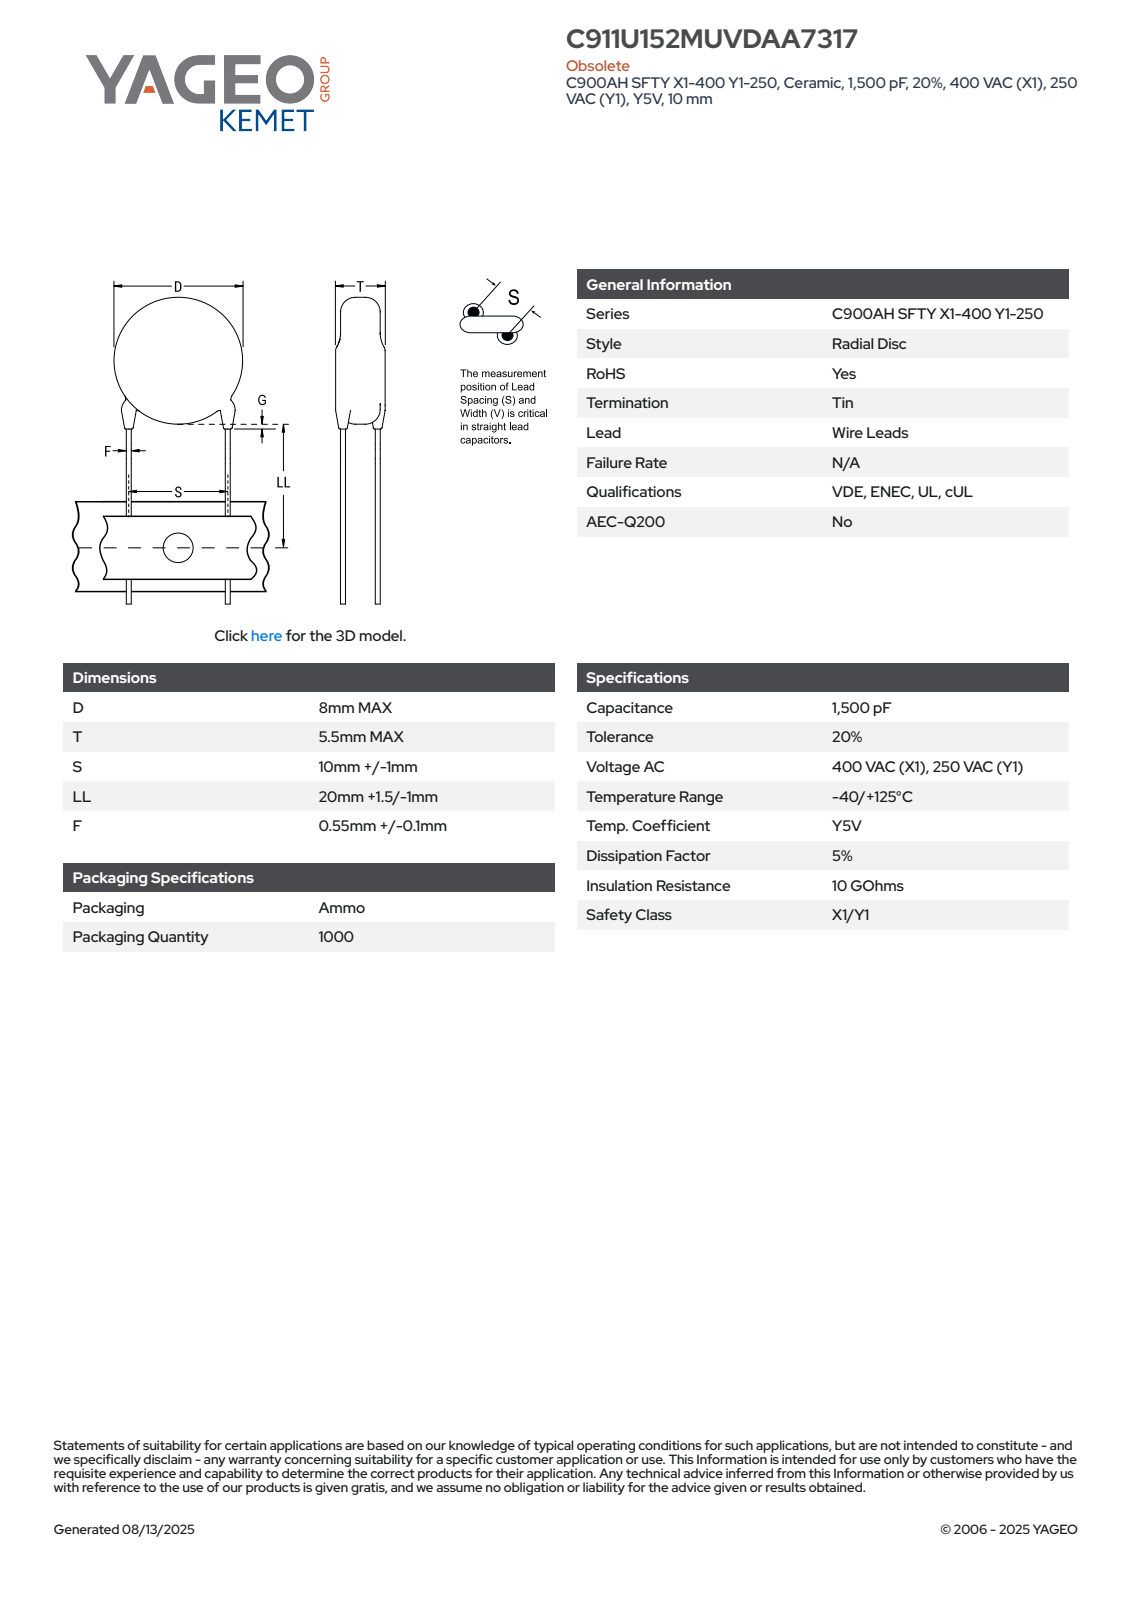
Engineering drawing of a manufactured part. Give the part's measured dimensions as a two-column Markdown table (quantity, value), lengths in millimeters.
| quantity | value |
| --- | --- |
| part name | CCD_STC900_D8T5.5S10LL21.5F0.65G3 |
| STEP written by | SolidWorks 2014 (AUTOMOTIVE_DESIGN) |
| units | millimeters |
| bodies | 4 solids, 83 faces (61 planar, 6 cylindrical, 16 other) |
| overall size | 29.5 × 9.17 × 6.36 |
| volume | 285 mm³ |
| surface area | 322 mm² |
| round bosses / shafts (diameter × count) | 0.65 × 2, 8 × 1 |
| main face-to-face distances | 5.5, 25.96, 25.04, 0.92, 0.4, 1.04, 3.77, 0.57, 2.73, 2.84 |
